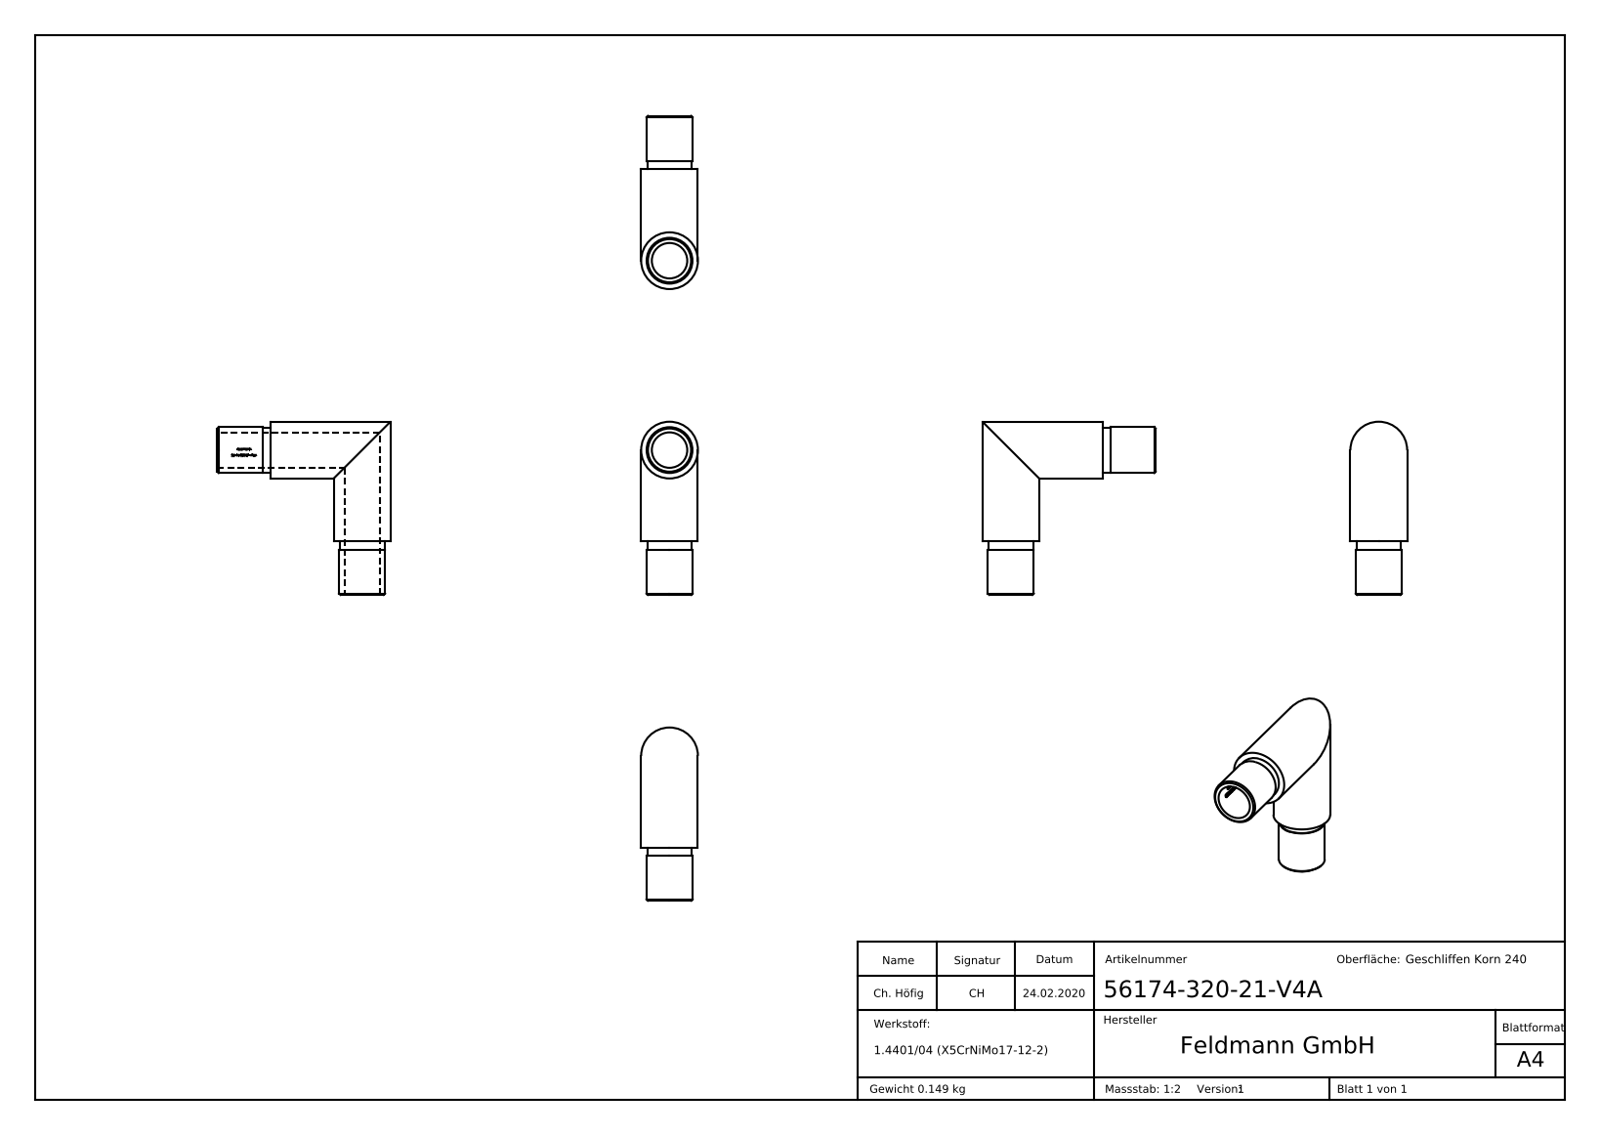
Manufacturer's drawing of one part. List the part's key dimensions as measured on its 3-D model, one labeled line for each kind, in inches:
Part name (STEP PRODUCT): 56174-320-21-V4A
STEP written by: SolidWorks 2015 (CONFIG_CONTROL_DESIGN)
Units: inches
Bodies: 1 solid, 300 faces (158 planar, 40 cylindrical, 102 other)
Overall size (bounding box): 2.559 × 2.559 × 0.839
Volume: 1.135 in³ · Surface area: 18.21 in²
Round holes (diameter × count): ⌀0.524 ×2
Round bosses / shafts (diameter × count): ⌀0.839 ×2, ⌀0.677 ×2, ⌀0.661 ×2
Partial cylindrical surfaces — rounded edges, fillets, slot ends (radius × count): R0.266 ×1
Main face-to-face distances: 0.787, 0.669, 0.118, 0.028, 0.103, 0.092, 0.021, 0.07, 0.025, 0.109
